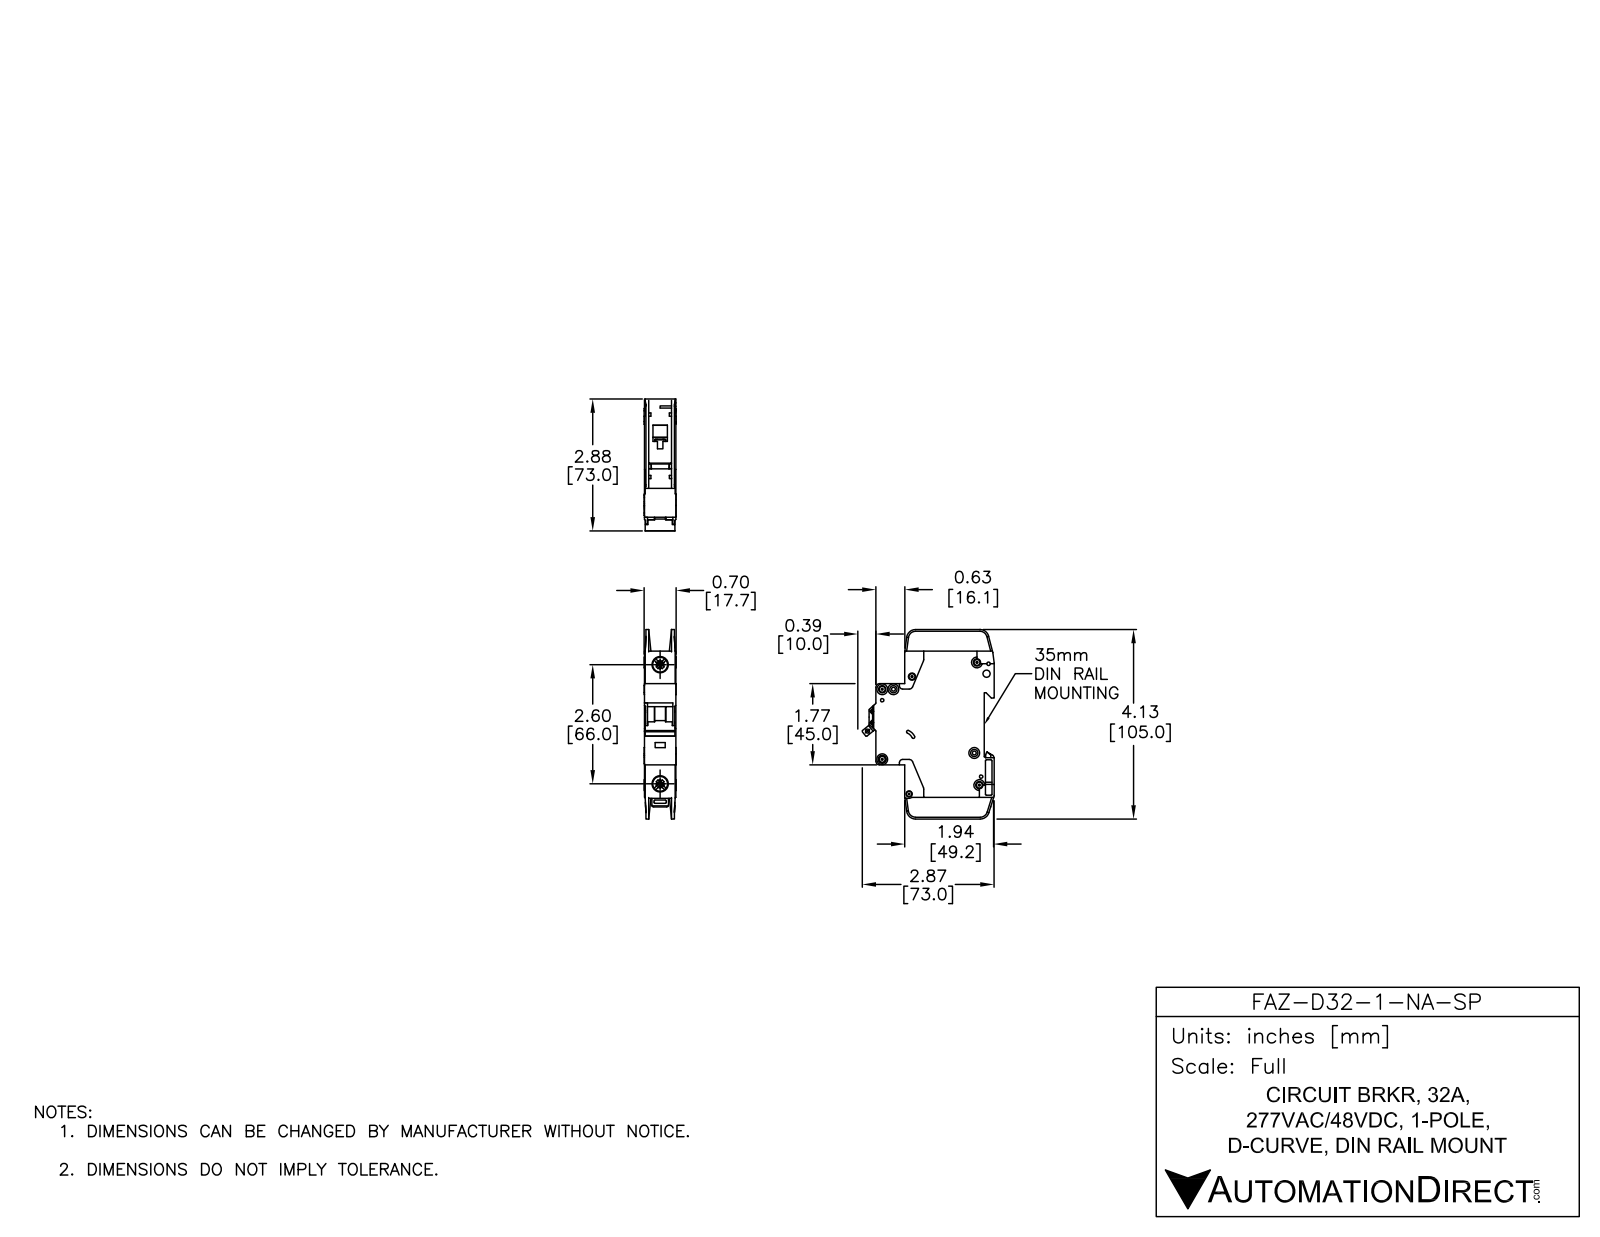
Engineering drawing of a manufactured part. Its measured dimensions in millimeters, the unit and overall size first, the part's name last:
Units: millimetres
Overall size (bounding box): 105 × 73.04 × 17.7
Round holes (diameter × count): ⌀3.6 ×7, ⌀1.09 ×2, ⌀1.5 ×2, ⌀4 ×2, ⌀7.15 ×2, ⌀8.2 ×2, ⌀1.9 ×1, ⌀2.15 ×1, ⌀2.2 ×1, ⌀2.55 ×1, ⌀3.3 ×1, ⌀3.4 ×1
Round bosses / shafts (diameter × count): ⌀6 ×7, ⌀2.5 ×1
Partial cylindrical surfaces — rounded edges, fillets, slot ends (radius × count): R0.25 ×29, R0.5 ×18, R1 ×10, R2 ×10, R5 ×5, R4 ×4, R1.8 ×3, R0.2 ×2
Main face-to-face distances: 17.5, 15.05, 0.7, 2.45, 1.75, 15.75, 13.3, 14, 12.6, 2
Hole centre spacings: 6.2, 5.19, 6.1, 8.19, 8.56, 8.7, 11.11, 12.45
Volume: 77 695 mm³ · Surface area: 24 740 mm²
Bodies: 3 solids, 784 faces (409 planar, 263 cylindrical, 112 other)
Part name (STEP PRODUCT): FAZ-D32-1-NA-SP
STEP written by: SolidWorks 2014 (AUTOMOTIVE_DESIGN)
